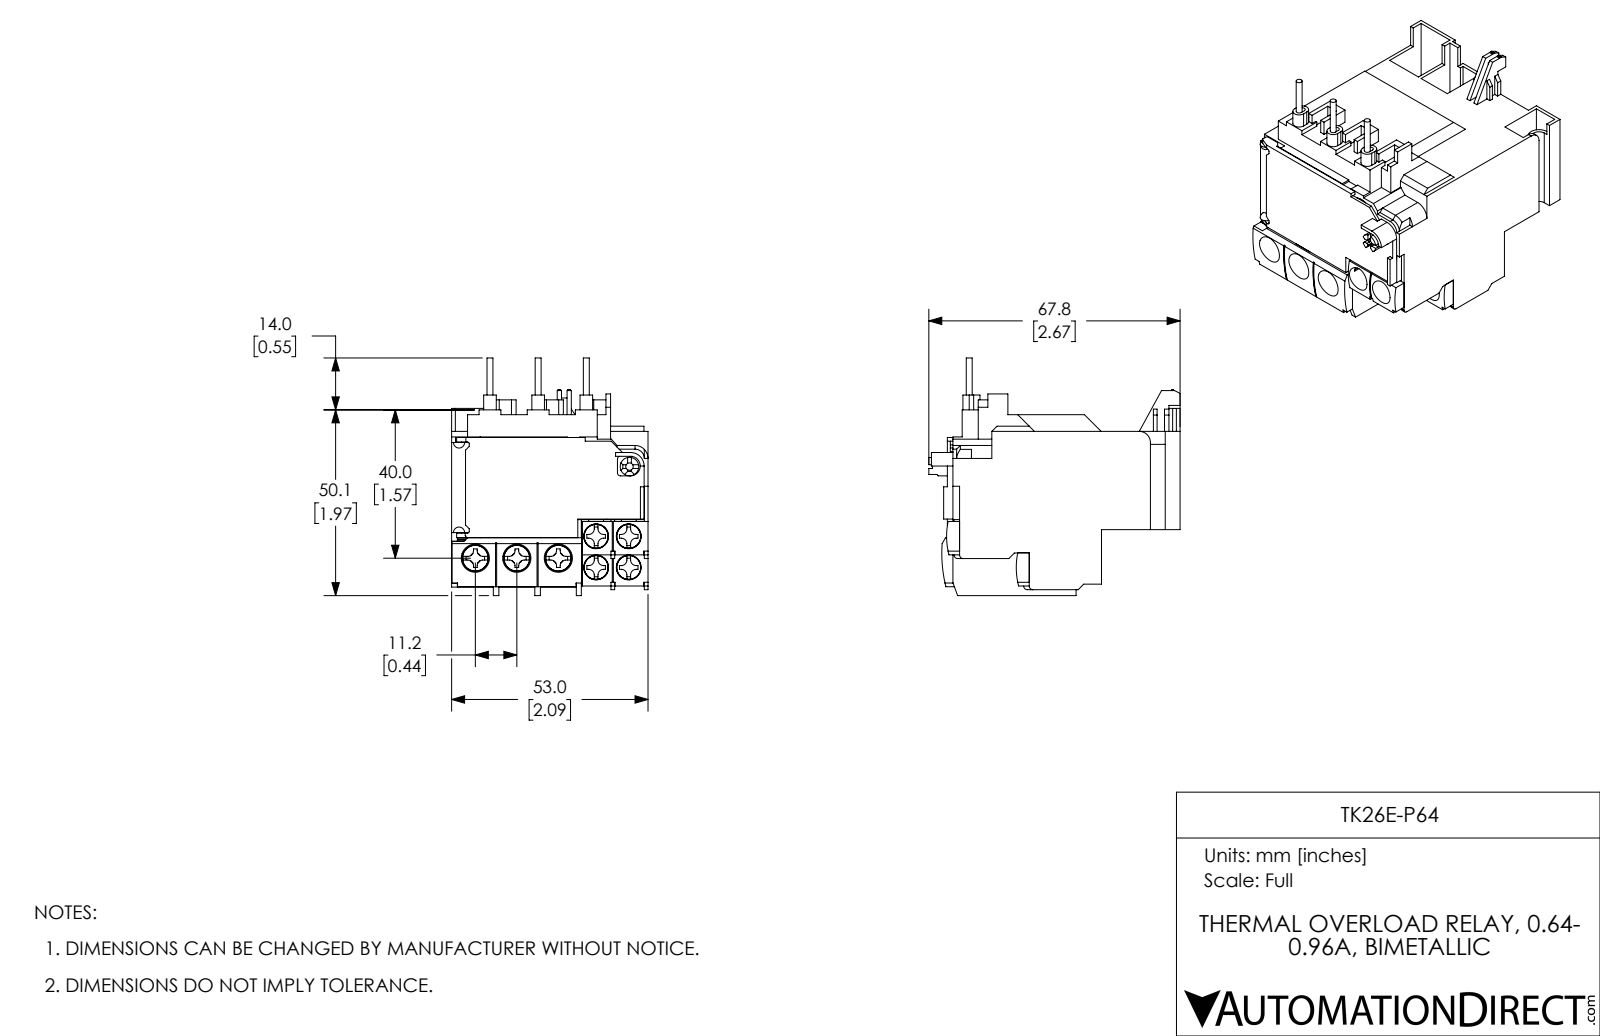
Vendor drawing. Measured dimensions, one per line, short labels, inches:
name: TK26E-P64
written by: SolidWorks 2017 (AUTOMOTIVE_DESIGN)
unit: in
bodies: 38 solids, 1480 faces (1225 planar, 220 cylindrical, 35 other)
size: 2.669 × 2.524 × 2.087
volume: 6.099 in³; area: 60.15 in²
holes: 4× ⌀0.138, 4× ⌀0.142, 4× ⌀0.264, 3× ⌀0.157, 3× ⌀0.161, 3× ⌀0.299, 1× ⌀0.039, 1× ⌀0.079, 1× ⌀0.197, 1× ⌀0.433
bosses: 4× ⌀0.26, 3× ⌀0.063, 1× ⌀0.236
rounds: 28× R0.059, 8× R0.039, 6× R0.02, 6× R0.067, 5× R0.031, 4× R0.047, 4× R0.171, 3× R0.189
face distances: 0.039, 0.354, 0.059, 0.472, 2.087, 0.079, 0.394, 0.433, 0.343, 0.028
hole spacings: 0.331, 0.346, 0.441, 0.479, 0.376, 0.413, 0.464, 0.74
